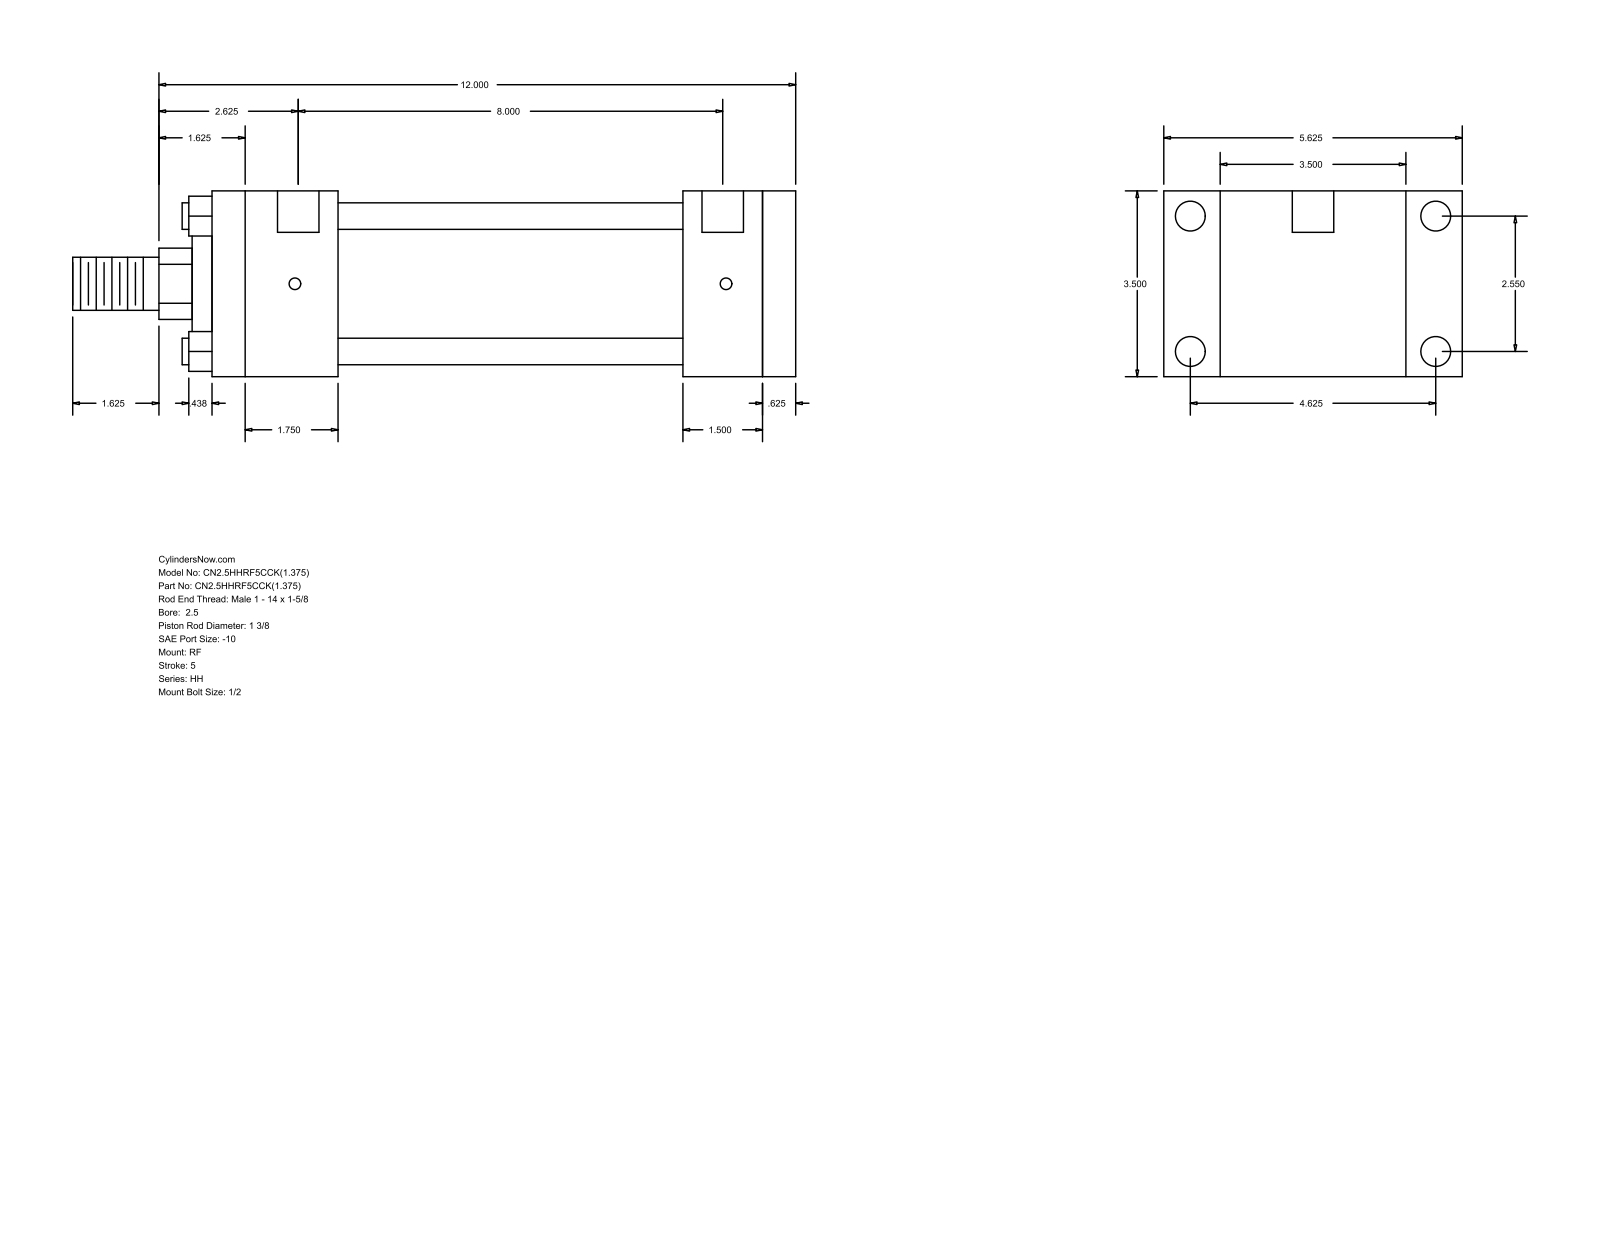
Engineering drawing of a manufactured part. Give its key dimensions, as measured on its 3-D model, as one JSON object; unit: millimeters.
{"part_name": "HH_RF__0250_1.375", "step_written_by": "GSSL Pune (CONFIG_CONTROL_DESIGN)", "units": "millimeters", "bodies": {"solids": 0, "faces": 92, "planar": 64, "cylindrical": 28, "other": 0}, "overall_size": [346.07, 142.88, 88.9], "round_holes": [[5.56, 4], [14.3, 4], [19.84, 2]], "round_bosses_or_shafts": [[12.7, 4], [73.03, 1], [50.8, 1], [34.92, 1], [25.4, 1]], "partial_cylinders_radius": [[17.06, 1]], "face_to_face_distances": [88.9, 279.4, 263.53, 15.87, 60.32, 203.21, 219.08, 225.42, 165.1, 38.11], "hole_center_spacings": [1.58, 64.76, 117.48, 134.15, 204.79, 206.37, 203.21]}
